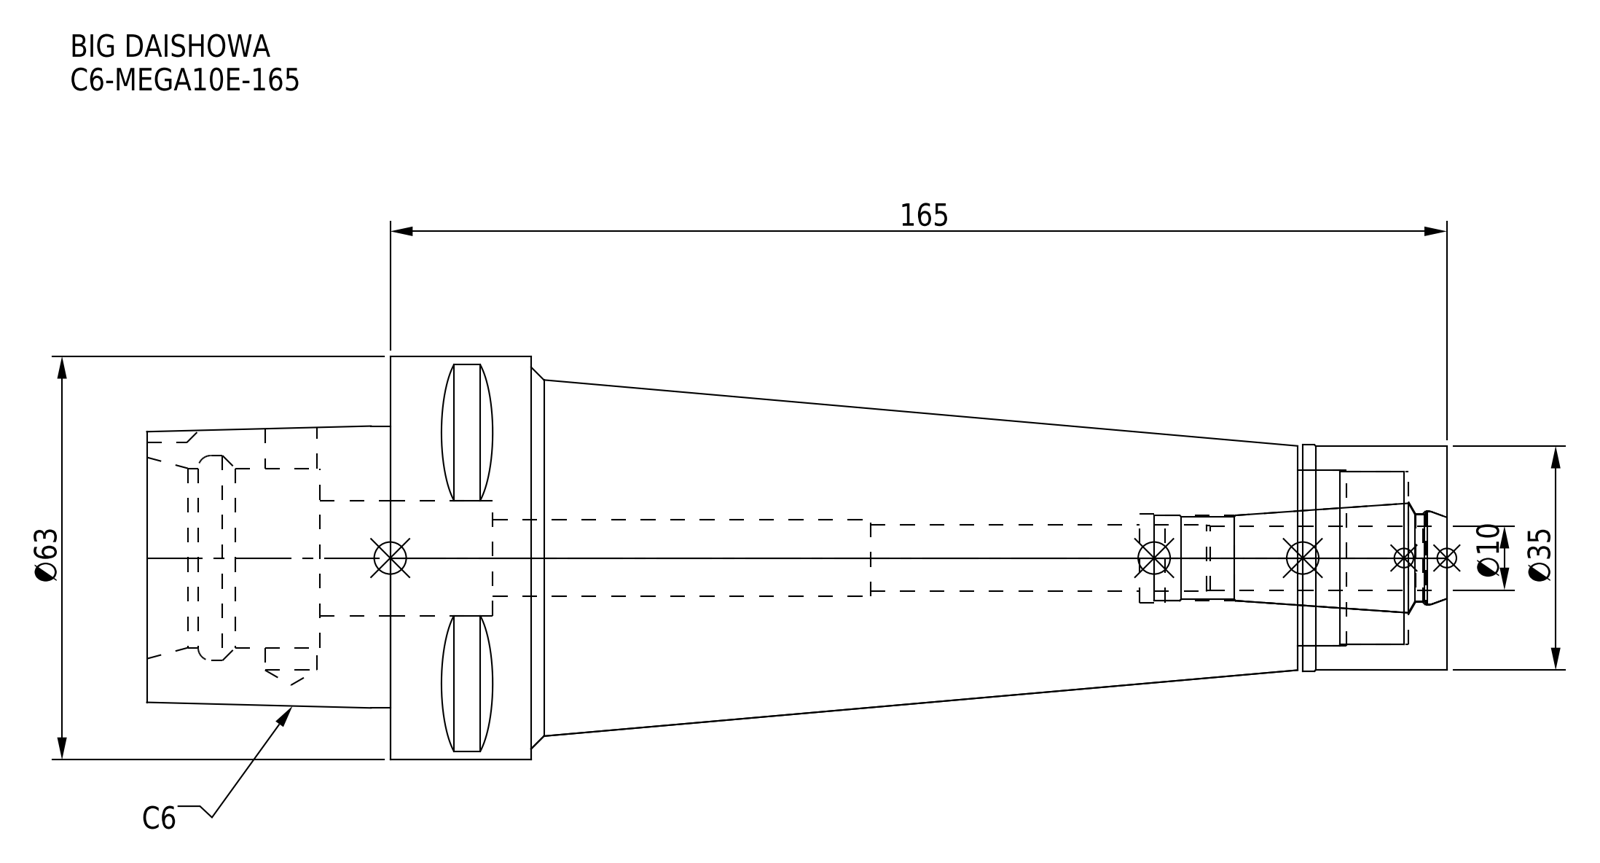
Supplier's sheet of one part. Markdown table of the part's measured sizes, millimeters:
| quantity | value |
| --- | --- |
| part name | C6-MEGA10E-165-100.stp; C6-MEGA10E-165_1.stp; C6-MEGA10E-165; MEN10_1.stp (+3 more) |
| STEP written by | SolidWorks 2019 (CONFIG_CONTROL_DESIGN) |
| units | millimeters |
| bodies | 2 solids, 100 faces (37 planar, 39 cylindrical, 24 other) |
| overall size | 203 × 63 × 63 |
| volume | 298 370 mm³ |
| surface area | 48 114 mm² |
| round holes (diameter × count) | 8.1 × 1, 10.4 × 1, 12 × 1, 13.3 × 1, 13.8 × 1, 13.9 × 1, 14.7 × 1, 18 × 1, 27 × 1, 27.5 × 1, 28 × 1, 32 × 1 |
| round bosses / shafts (diameter × count) | 63 × 1, 35.3 × 1, 35 × 1 |
| partial cylindrical surfaces (radius × count) | 5 × 1 |
| main face-to-face distances | 165, 38, 27, 203, 6, 143, 22.5, 142.5, 180.5, 23.3 |
